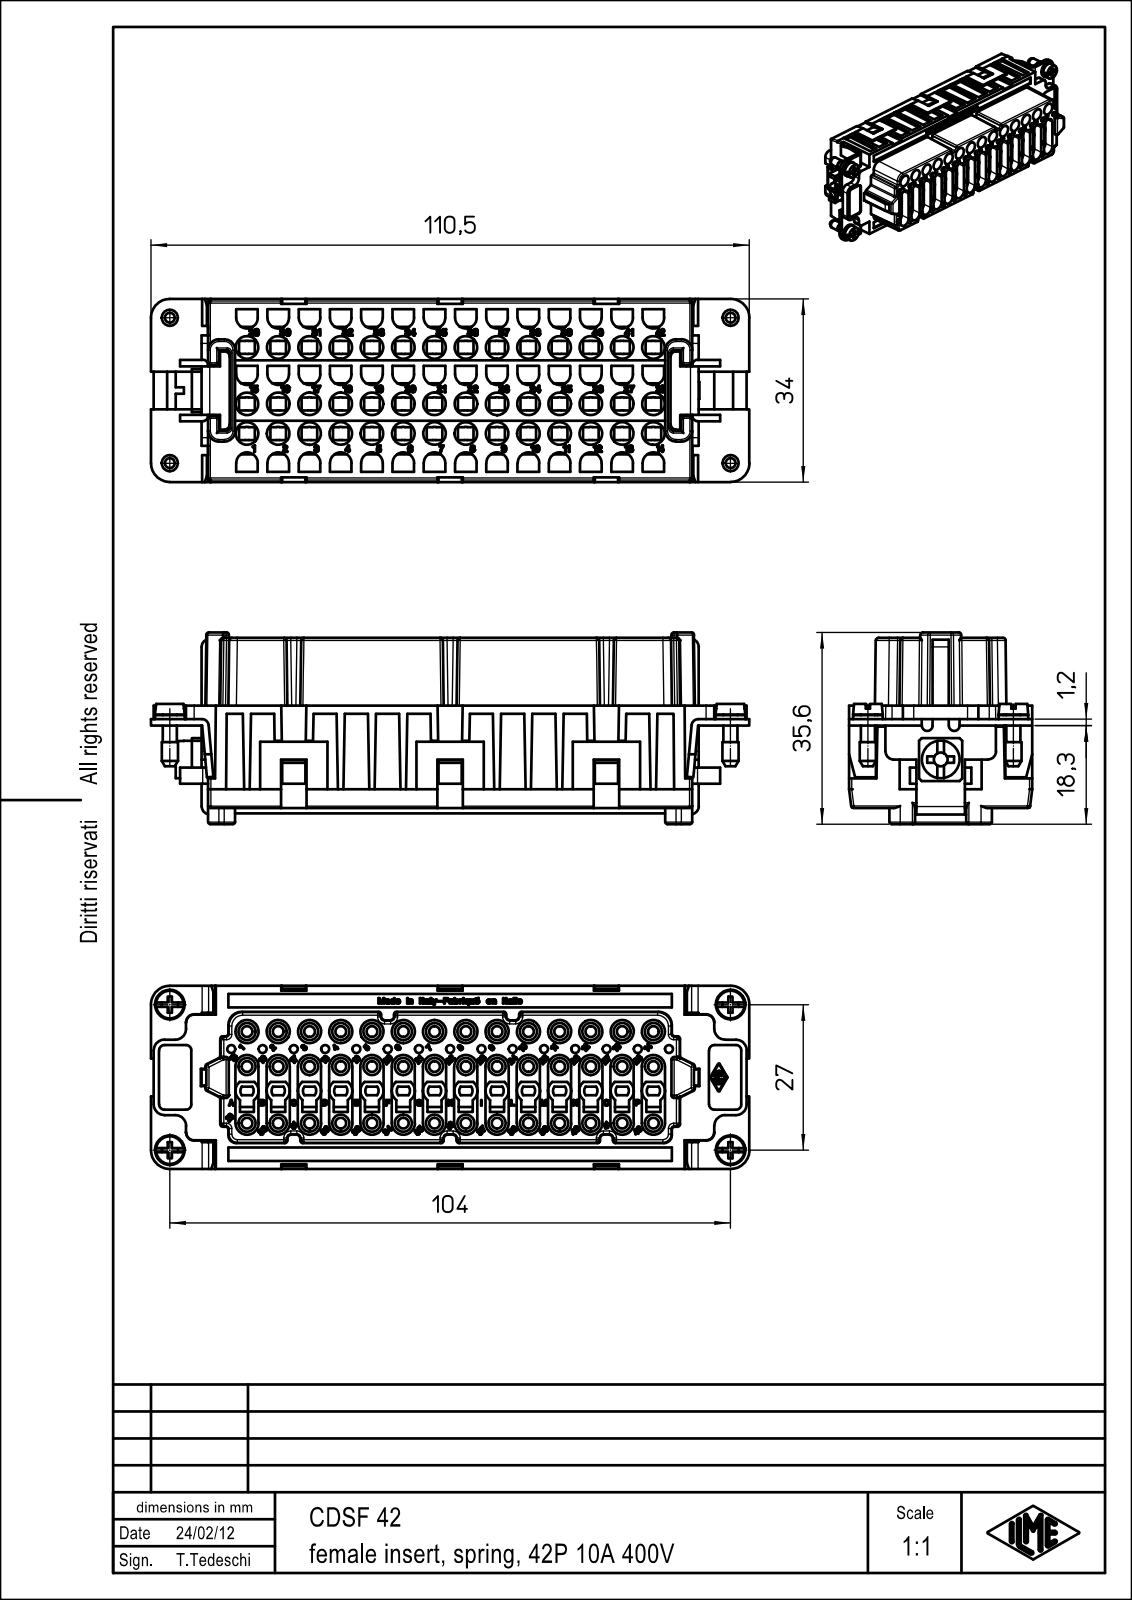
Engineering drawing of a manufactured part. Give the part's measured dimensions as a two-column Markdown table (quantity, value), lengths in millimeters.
| quantity | value |
| --- | --- |
| part name | CDSF_42 |
| STEP written by | Creo Elements/Direct Modeling 17.0D 15-Jul-2011 (C) Parametric Technology GmbH (AUTOMOTIVE_DESIGN) |
| units | millimeters |
| bodies | 1 solid, 10493 faces (9588 planar, 592 cylindrical, 313 other) |
| overall size | 111 × 35.6 × 34 |
| volume | 74 161 mm³ |
| surface area | 31 238 mm² |
| round holes (diameter × count) | 2 × 42, 4.2 × 42, 1.5 × 15, 4.3 × 14, 2.58 × 1, 3 × 1 |
| round bosses / shafts (diameter × count) | 5.5 × 4, 3 × 4, 2.6 × 4, 7 × 1 |
| partial cylindrical surfaces (radius × count) | 0.5 × 58, 2 × 58, 2.15 × 42, 1 × 20, 0.4 × 18, 1.25 × 14, 1.5 × 14, 0.8 × 10 |
| main face-to-face distances | 0.9, 1.2, 33.1, 1, 29, 16.3, 11.5, 18.7, 32.2, 31.6 |
| hole center spacings | 4.36, 14.86, 9.29, 26.3, 5.8, 11.6, 20.56, 23.2 |
